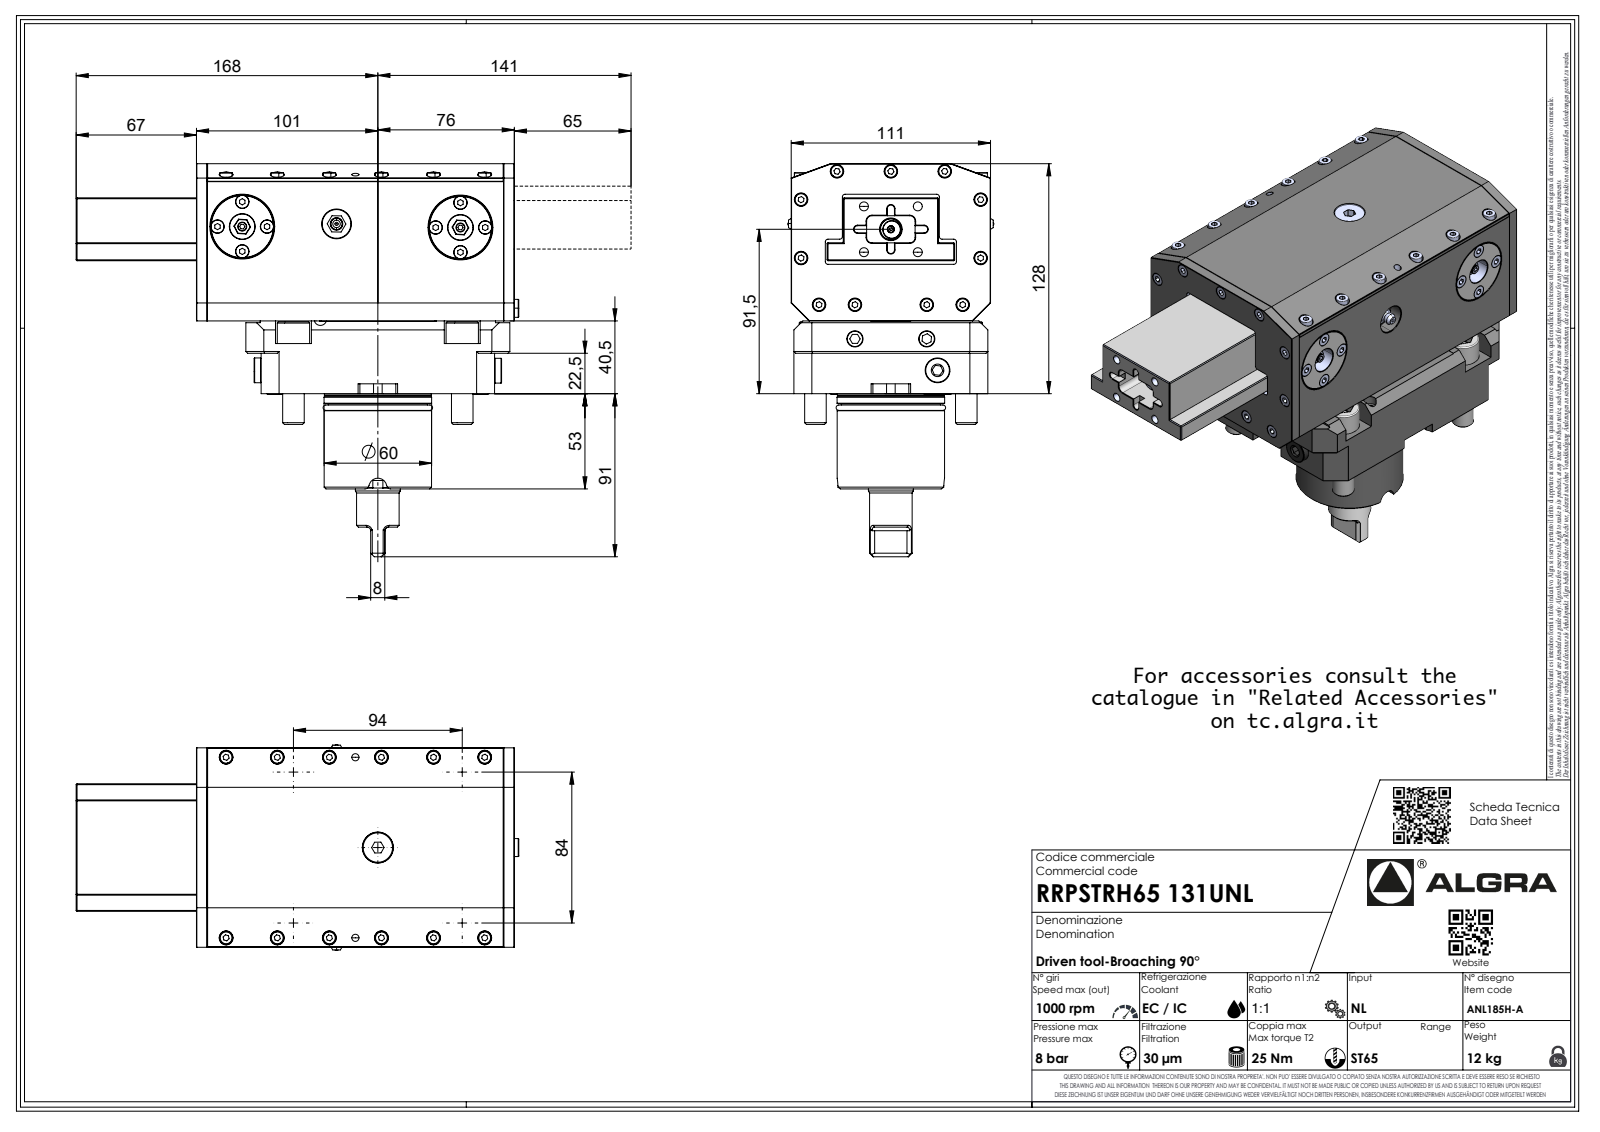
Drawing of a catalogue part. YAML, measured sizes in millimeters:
part_name: "RRPSTRH65131UNL"
step_written_by: "SolidWorks 2023 (AUTOMOTIVE_DESIGN)"
units: millimeters
bodies: {solids: 1, faces: 848, planar: 546, cylindrical: 149, other: 153}
overall_size: [246.47, 218.76, 114.6]
volume: 2541000
surface_area: 158859
round_holes:
  - {diameter: 35.5, count: 2}
  - {diameter: 3.15, count: 1}
  - {diameter: 16, count: 1}
  - {diameter: 61, count: 1}
round_bosses_or_shafts:
  - {diameter: 18, count: 4}
  - {diameter: 12, count: 4}
  - {diameter: 59.9, count: 1}
  - {diameter: 59.8, count: 1}
  - {diameter: 59.5, count: 1}
  - {diameter: 55.2, count: 1}
  - {diameter: 55, count: 1}
  - {diameter: 25, count: 1}
partial_cylinders:
  - {radius: 8, count: 20}
  - {radius: 3.5, count: 12}
  - {radius: 3.6, count: 8}
  - {radius: 0.5, count: 7}
  - {radius: 0.78, count: 7}
  - {radius: 5.55, count: 7}
  - {radius: 10, count: 4}
  - {radius: 2, count: 2}
face_to_face_distances: [111, 87.5, 40.5, 128, 1.5, 109.5, 177, 35, 68.5, 40.3]
hole_center_spacings: [16.58, 52.52, 54.65, 69.03, 70.49, 121.5]
